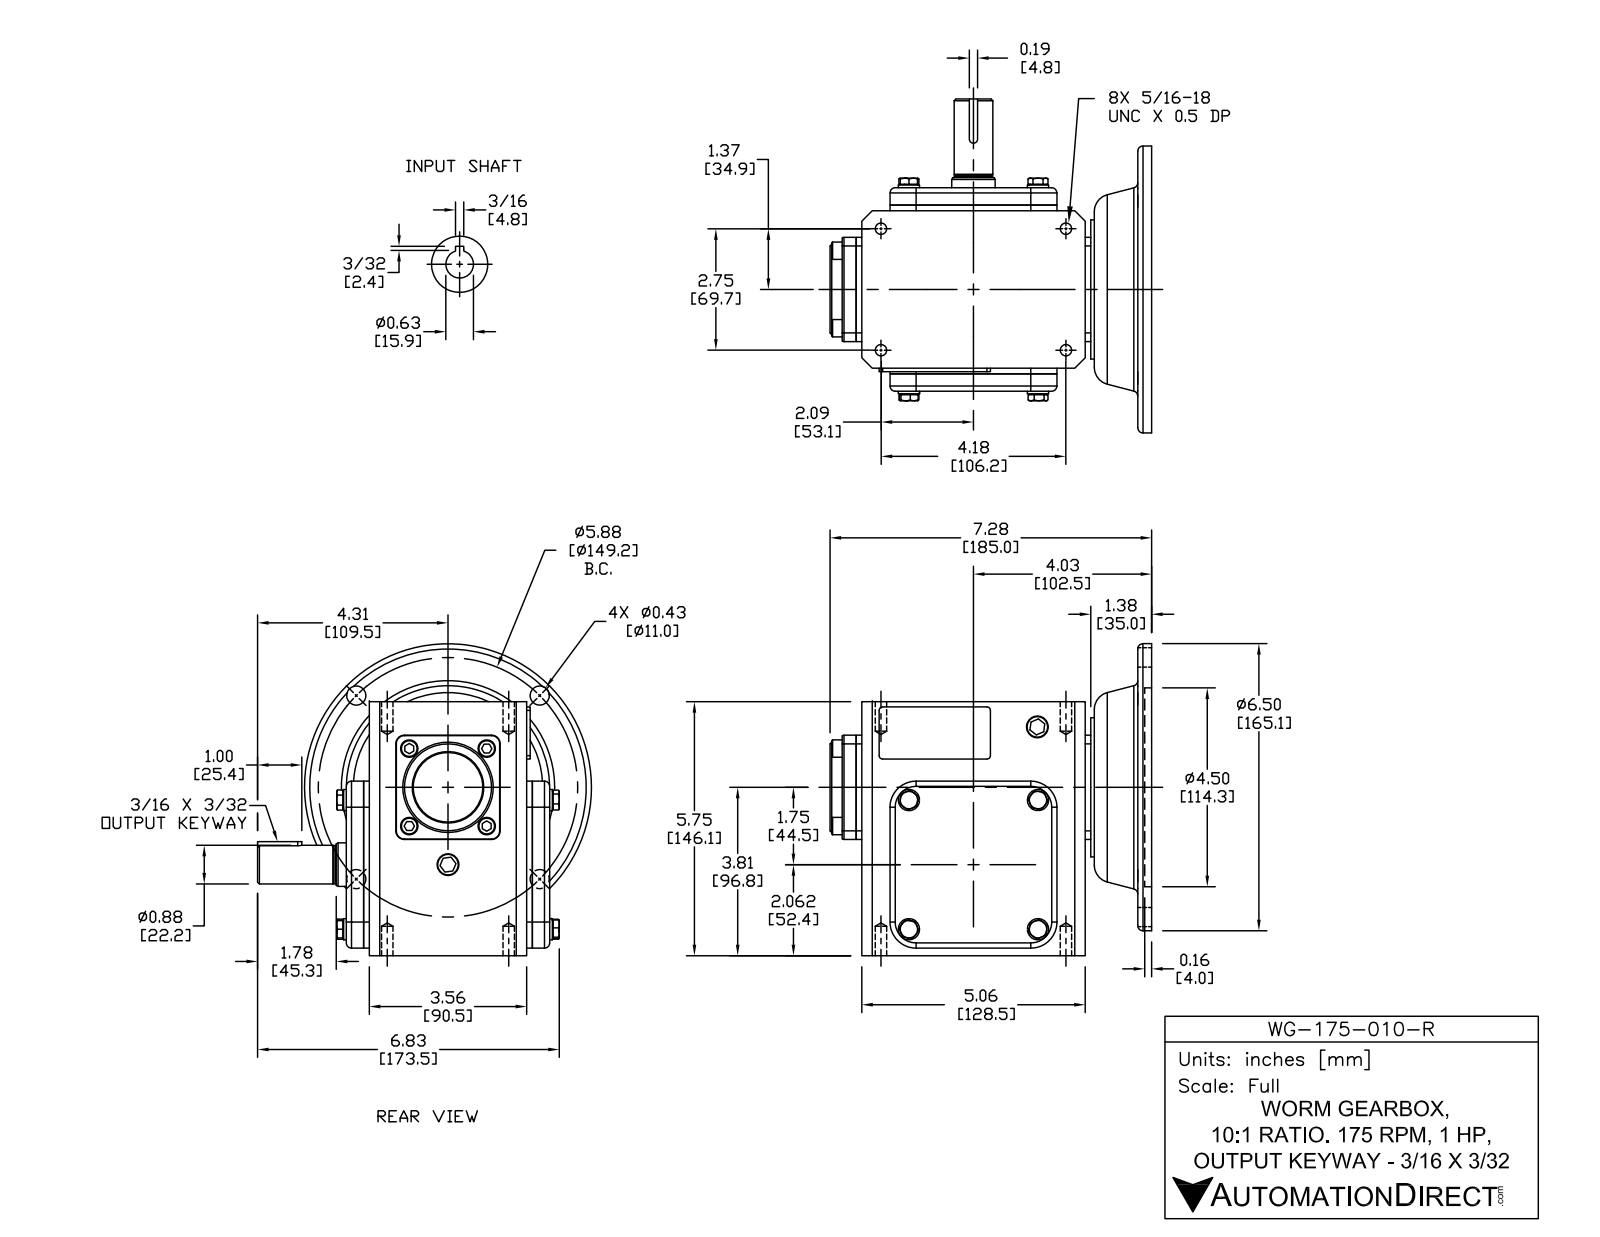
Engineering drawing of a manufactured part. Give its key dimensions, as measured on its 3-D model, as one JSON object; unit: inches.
{"part_name": "WG-175-010-R", "step_written_by": "SolidWorks 2015 (CONFIG_CONTROL_DESIGN)", "units": "inches", "bodies": {"solids": 43, "faces": 613, "planar": 312, "cylindrical": 172, "other": 129}, "overall_size": [7.559, 7.283, 7.06], "volume_in3": 131.9, "surface_area_in2": 366.4, "round_holes": [[0.257, 4], [0.406, 4], [0.512, 1], [0.625, 1], [0.984, 1], [1.181, 1], [1.457, 1], [1.575, 1], [3.543, 1], [4.5, 1]], "round_bosses_or_shafts": [[0.394, 8], [0.48, 4], [0.512, 2], [6.496, 1], [3.15, 1], [2.047, 1], [1.575, 1], [0.875, 1]], "partial_cylinders_radius": [[0.079, 8], [0.118, 8], [0.197, 4], [0.591, 4], [0.02, 2], [0.039, 2], [0.094, 1]], "face_to_face_distances": [0.128, 3.819, 4.213, 0.394, 4.085, 3.691, 0.522, 0.315, 5.75, 6.693], "hole_center_spacings": [2.937, 4.154, 2.103, 2.75, 4.188, 4.354, 5.01, 5.875]}
